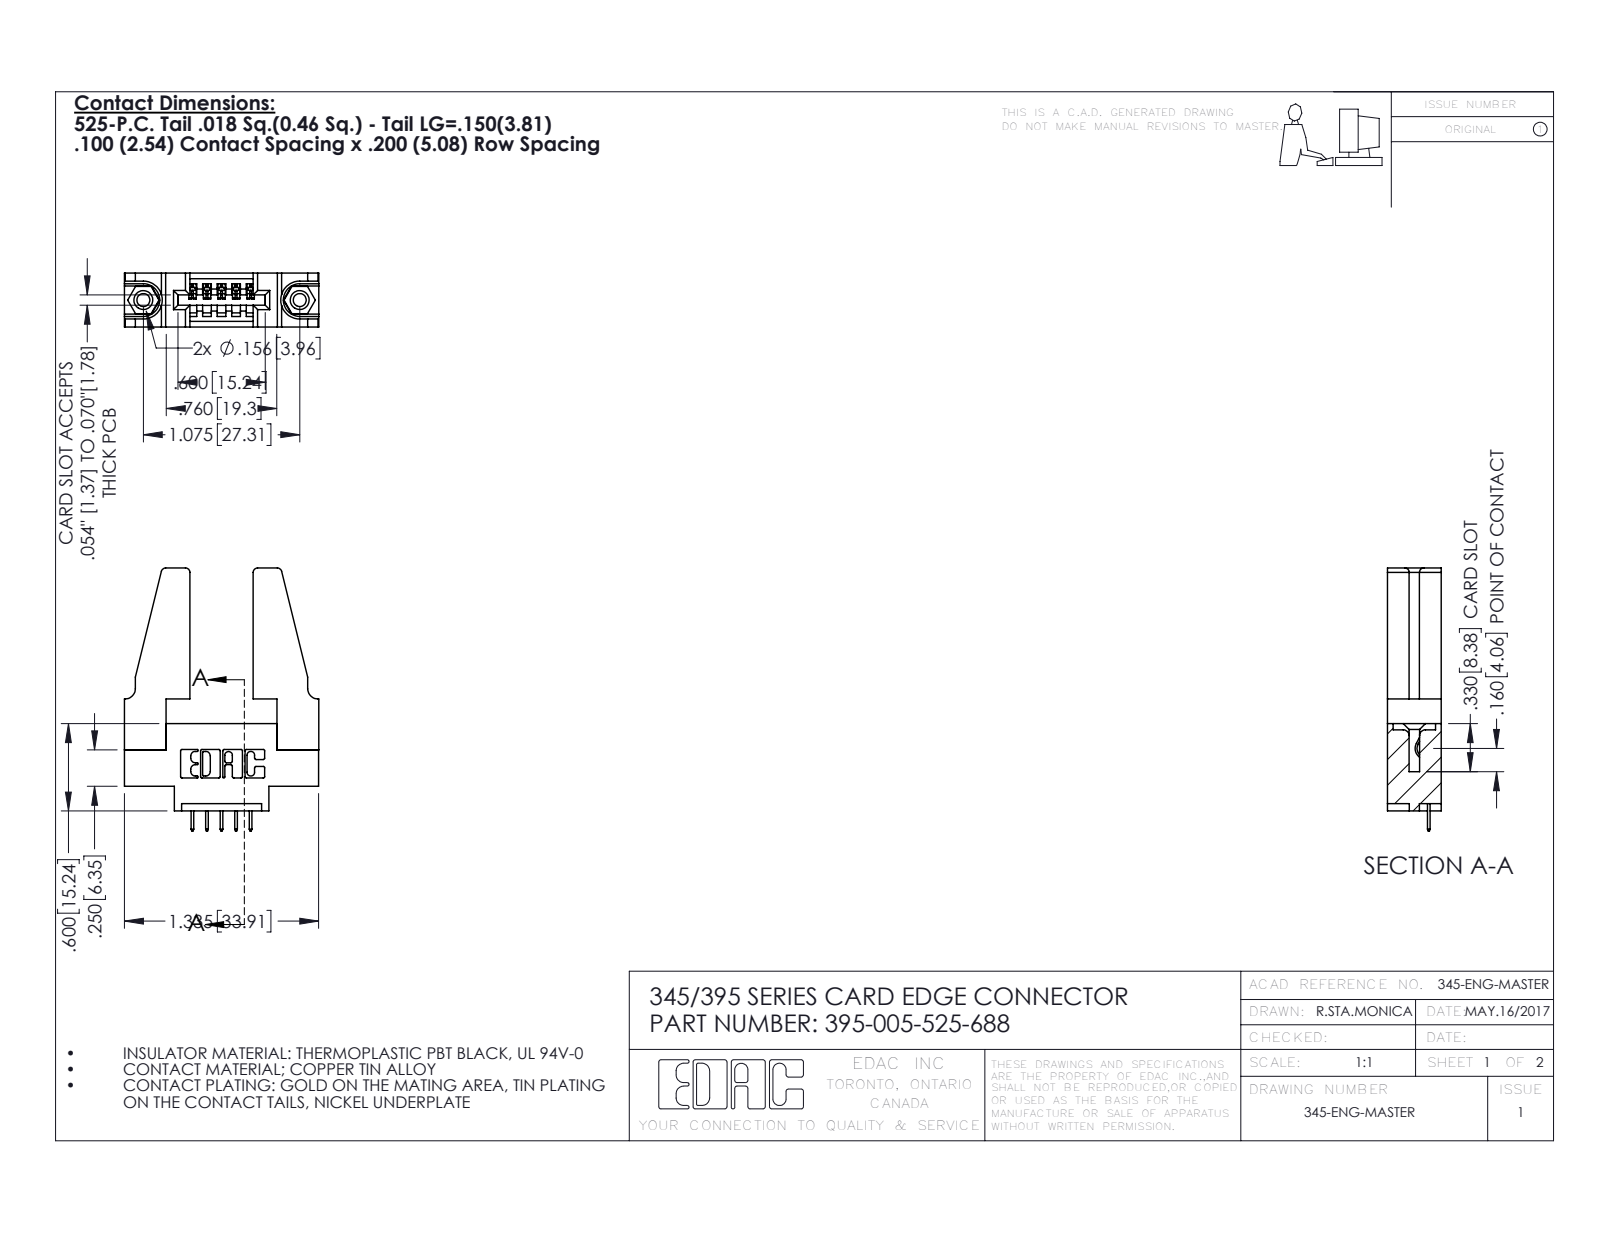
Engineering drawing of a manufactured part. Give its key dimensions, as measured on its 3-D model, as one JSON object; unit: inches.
{"part_name": "345-220-078_345-220-088; 345-250-001_345-250-001-102; 395-005-525-688; 345 Part_0.170 Offset - 0.156 Dia-TH (+1 more)", "step_written_by": "SolidWorks 2020 (CONFIG_CONTROL_DESIGN)", "units": "inches", "bodies": {"solids": 10, "faces": 564, "planar": 386, "cylindrical": 162, "other": 16}, "overall_size": [1.807, 1.336, 0.37], "volume_in3": 0.369, "surface_area_in2": 9.901, "round_holes": [[0.089, 2], [0.125, 2], [0.156, 2], [0.064, 1]], "round_bosses_or_shafts": [[0.155, 2]], "partial_cylinders_radius": [[0.01, 22], [0.006, 10], [0.03, 8], [0.007, 6], [0.031, 6], [0.026, 3], [0.031, 2], [0.04, 2]], "face_to_face_distances": [0.37, 0.072, 0.298, 0.2, 0.148, 0.15, 0.22, 0.077, 0.435, 0.288], "hole_center_spacings": [0.27, 0.847, 1.075]}
